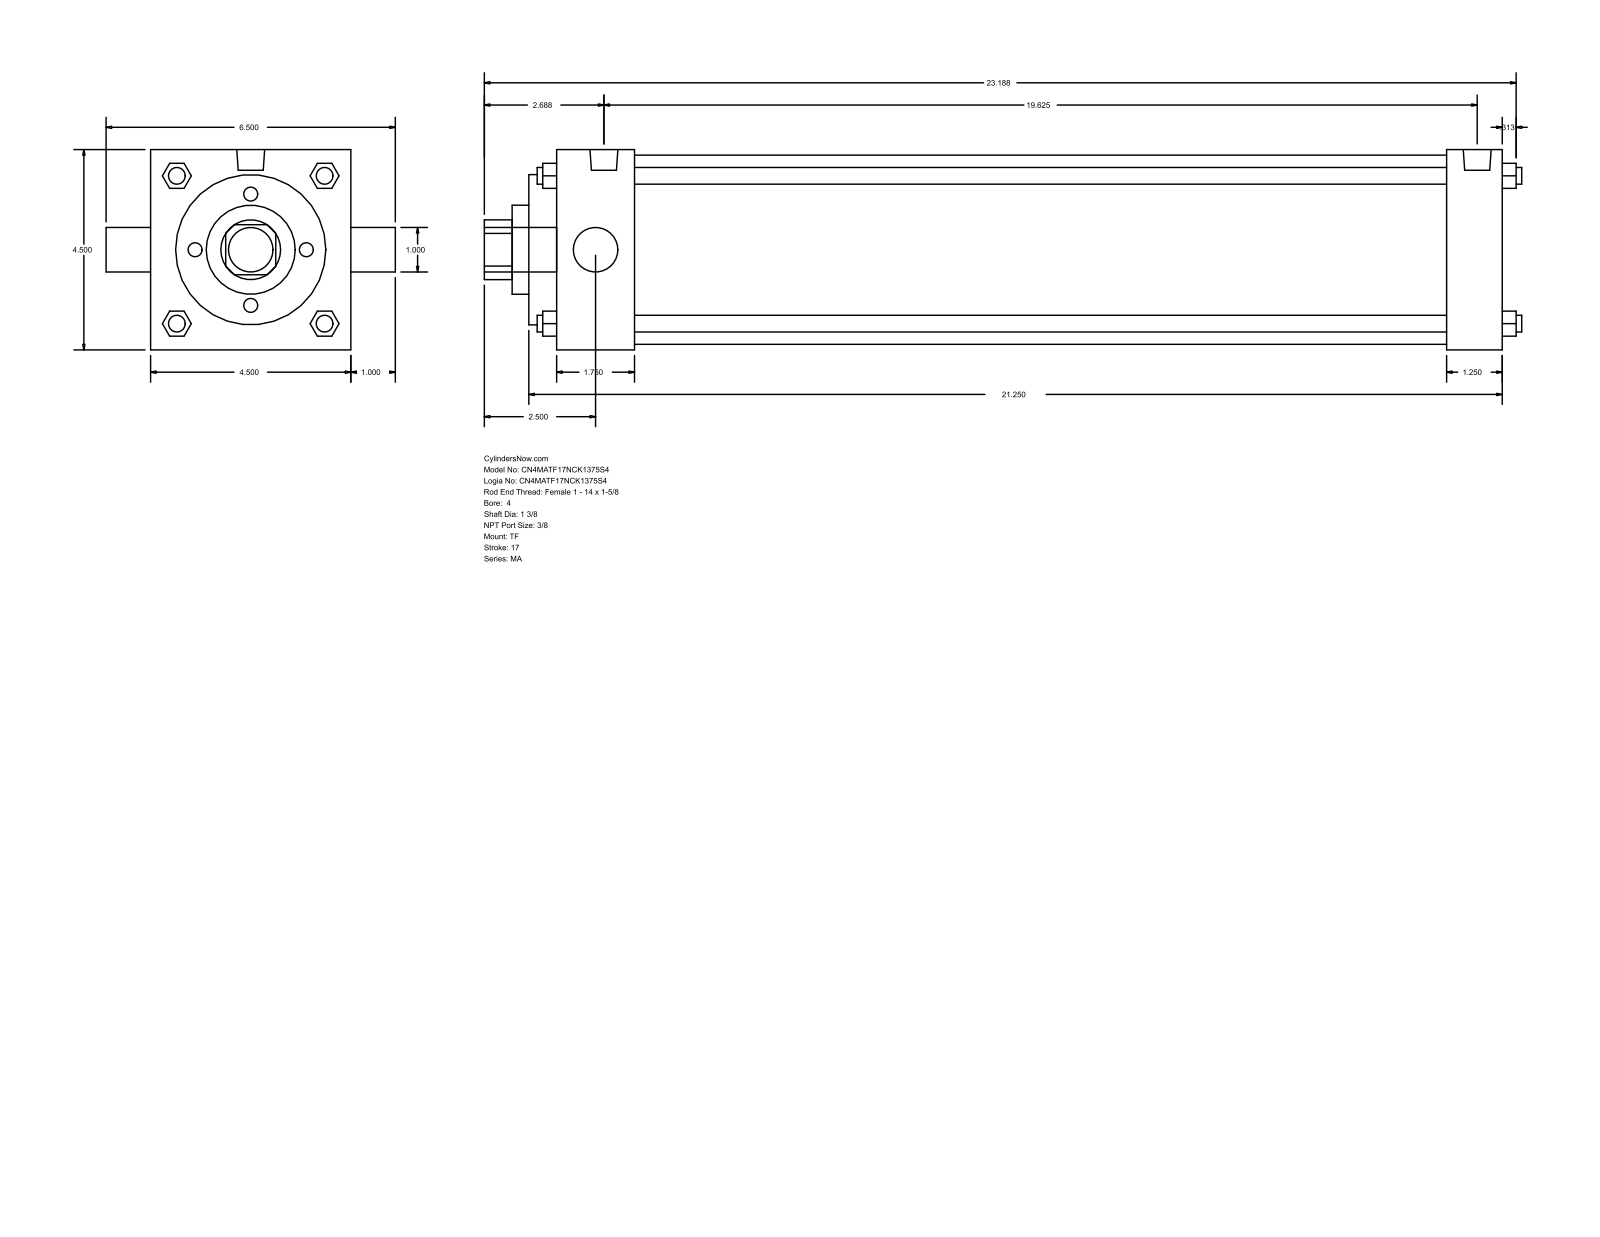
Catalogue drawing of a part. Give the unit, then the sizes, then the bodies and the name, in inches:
Units: inches
Overall size (bounding box): 23.313 × 6.5 × 4.5
Round holes (diameter × count): ⌀1 ×1, ⌀1.375 ×1, ⌀2 ×1, ⌀3.375 ×1, ⌀4.25 ×1
Round bosses / shafts (diameter × count): ⌀0.375 ×4, ⌀0.437 ×3, ⌀0.627 ×2, ⌀1 ×1
Partial cylindrical surfaces — rounded edges, fillets, slot ends (radius × count): R0.672 ×1
Main face-to-face distances: 4.5, 21.25, 21.875, 0.625, 20.625, 20, 1.25, 2.375, 1.75, 18.25
Bodies: 0 solids, 122 faces (93 planar, 29 cylindrical, 0 other)
Part name (STEP PRODUCT): MA_TF__0400_1.375
STEP written by: GSSL Pune (CONFIG_CONTROL_DESIGN)
